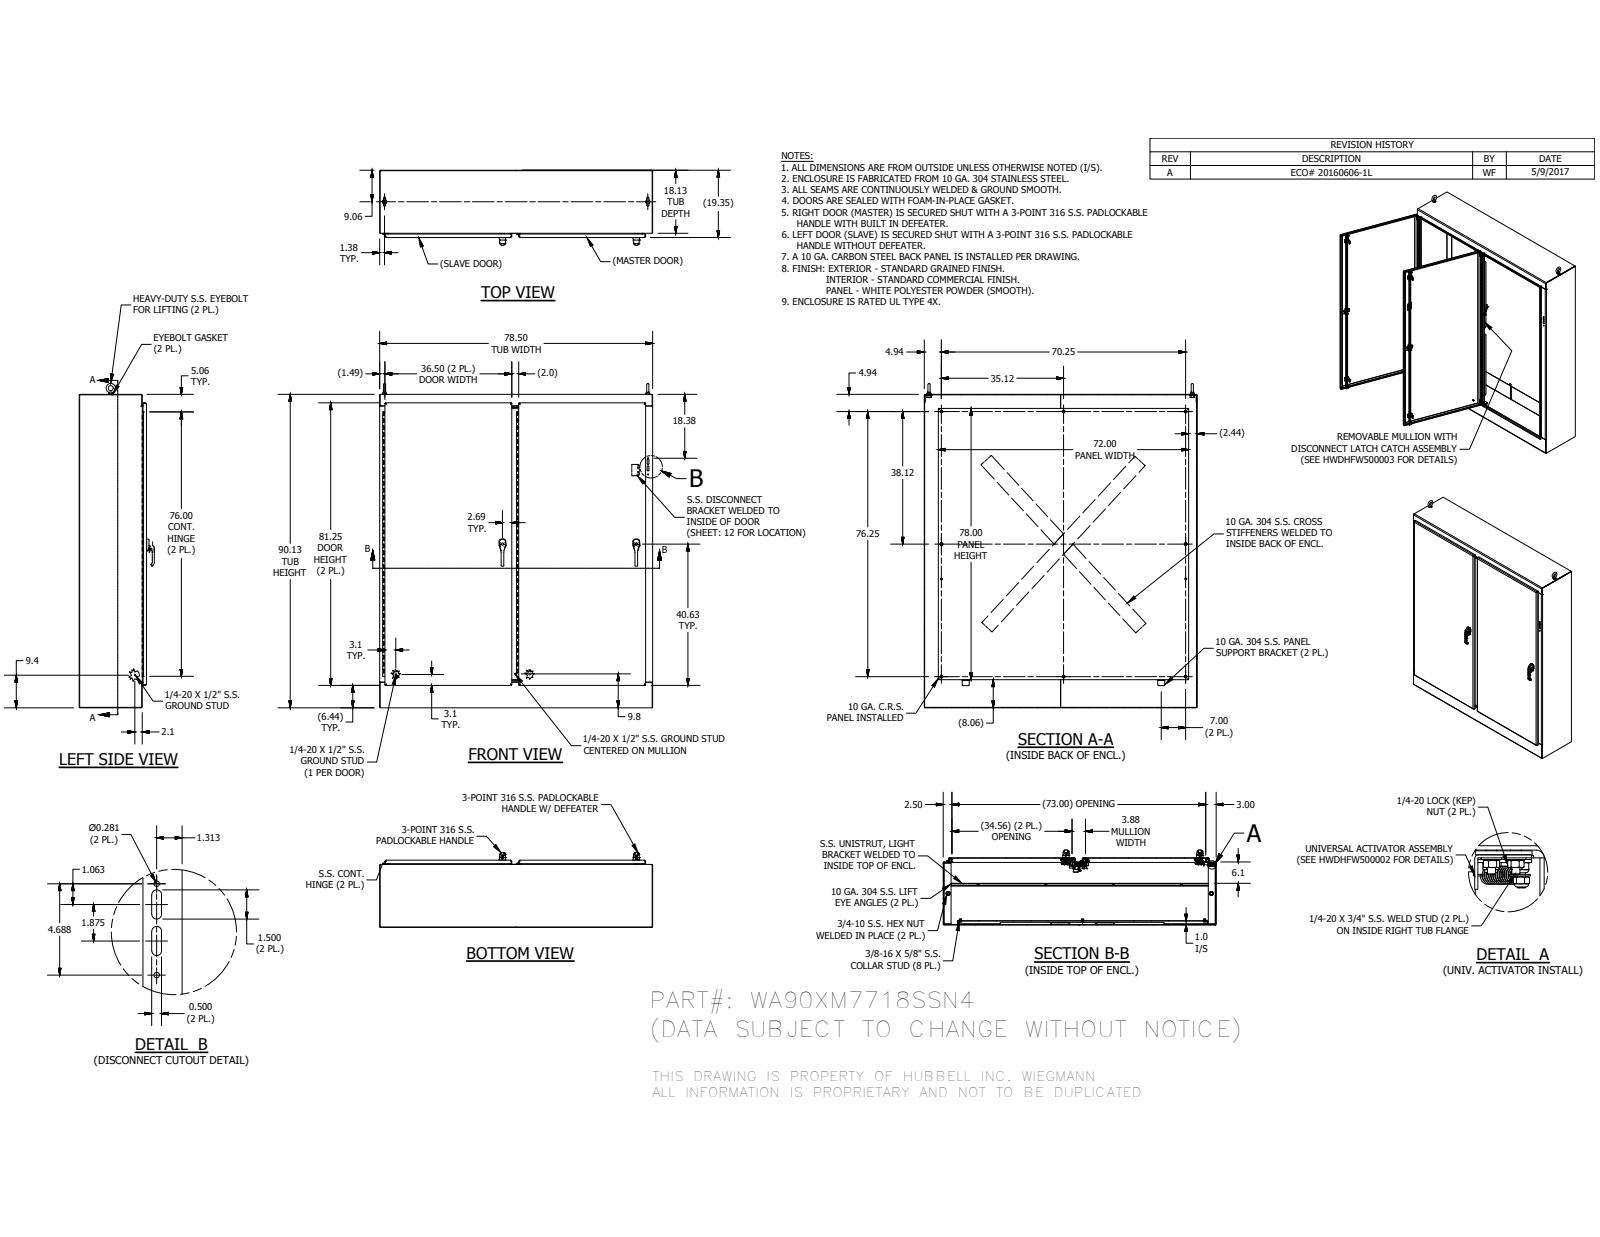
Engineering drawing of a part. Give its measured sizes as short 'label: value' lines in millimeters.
name: WA90XM18SSN4LS; WA90XM77SSN4HFB; WAXM7718SSN4TOP; WAXM7718SSN4BTM (+8 more)
written by: Autodesk Inventor 2016 (AUTOMOTIVE_DESIGN)
unit: mm
bodies: 258 solids, 10914 faces (5214 planar, 3572 cylindrical, 2128 other)
size: 2368.49 × 1993.9 × 548.62
volume: 66 370 000 mm³; area: 39 120 000 mm²
holes: 48× ⌀3.55, 18× ⌀9.52, 16× ⌀6.35, 10× ⌀14.29, 9× ⌀4.76, 8× ⌀3.45, 8× ⌀4.17, 8× ⌀4.83, 8× ⌀4.98, 8× ⌀5.1, 8× ⌀6.65, 8× ⌀7.33
bosses: 18× ⌀8.38, 18× ⌀6.35, 13× ⌀15.88, 12× ⌀8.56, 11× ⌀9.52, 9× ⌀14.29, 8× ⌀7.11, 8× ⌀6.02
rounds: 358× R0.5, 222× R0.3, 192× R0.51, 47× R3.17, 42× R0.47, 36× R1.59, 31× R6.35, 28× R1.27
face distances: 3.4, 488.1, 3.41, 484.7, 25.4, 491.5, 28.8, 462.7, 32.21, 28.81
hole spacings: 0.45, 973.57, 973.64, 973.42, 973.35, 973.72, 973.79, 1829.12
